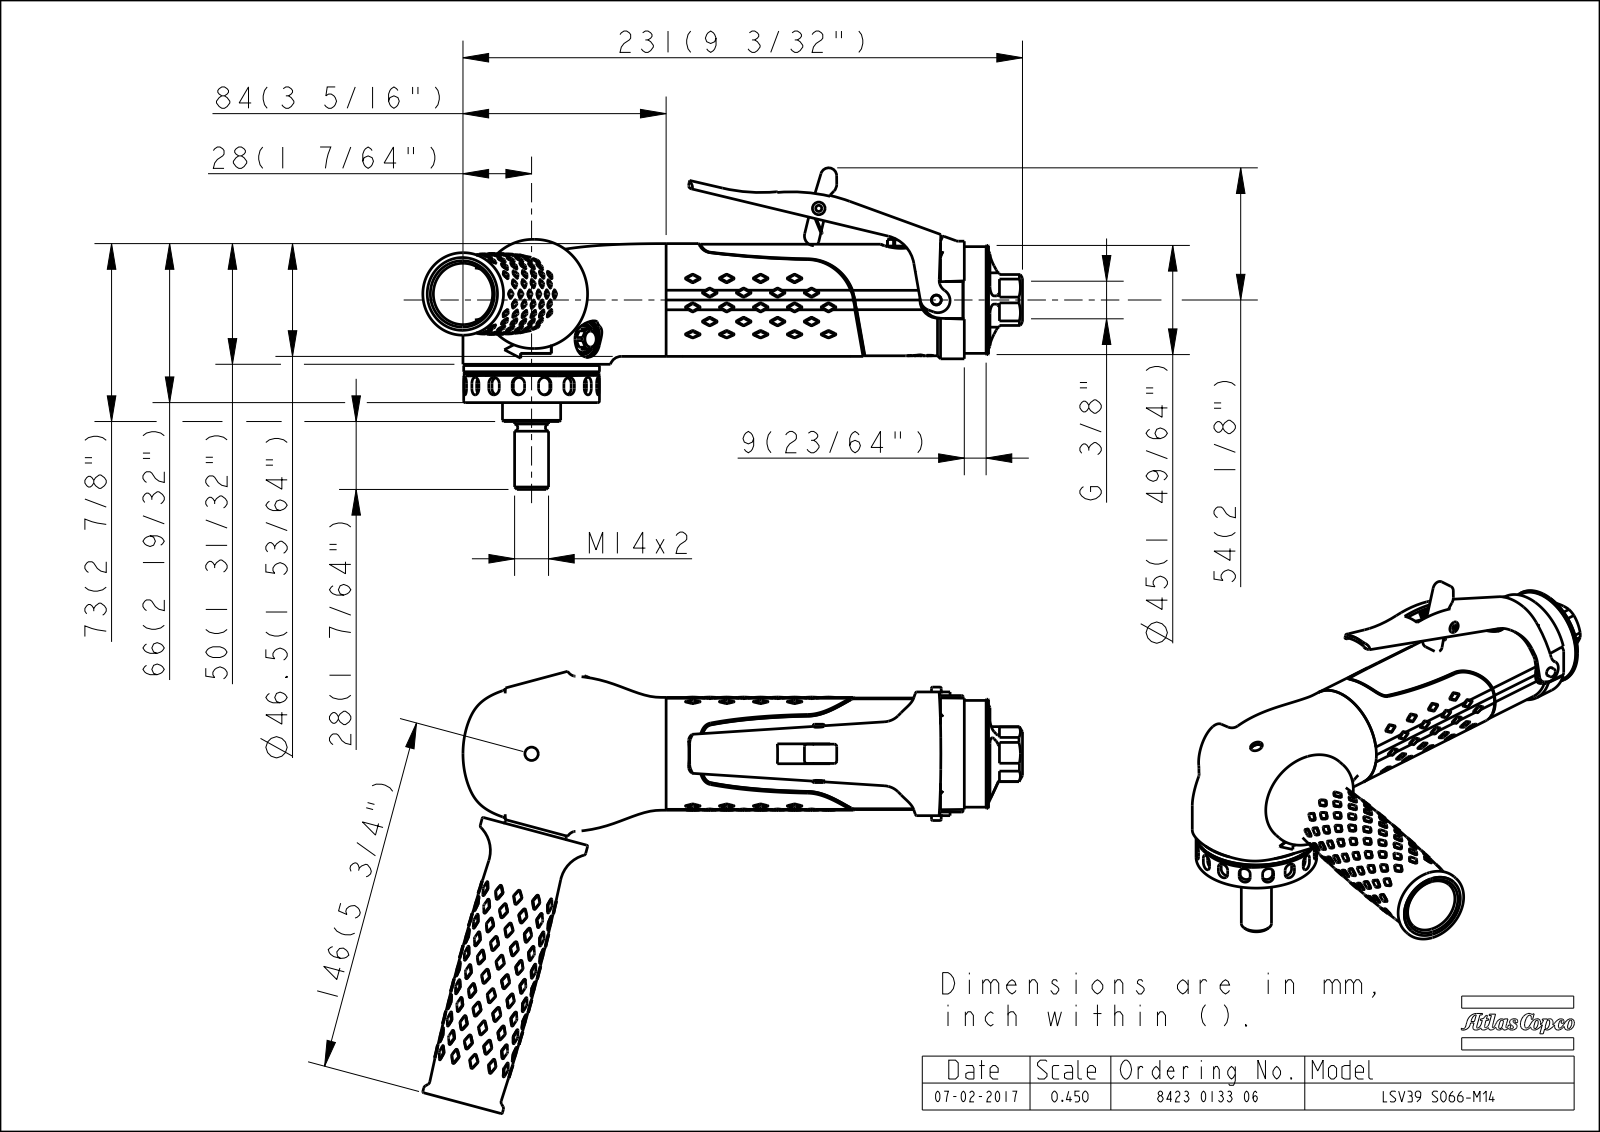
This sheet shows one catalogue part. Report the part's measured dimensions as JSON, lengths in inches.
{"part_name": "4150178903; 4150178984_ASM; 4150225400_SPEC_AF2; 4150225440_AF2 (+8 more)", "step_written_by": "CREO PARAMETRIC BY PTC INC, 2014440 (CONFIG_CONTROL_DESIGN)", "units": "inches", "bodies": {"solids": 30, "faces": 4762, "planar": 1235, "cylindrical": 1015, "other": 2512}, "overall_size": [9.739, 7.178, 5.22], "volume_in3": 16.82, "surface_area_in2": 993.2, "round_holes": [[0.118, 5], [0.197, 5], [0.165, 4], [0.492, 3], [0.106, 2], [0.217, 2], [0.331, 2], [0.335, 2], [0.591, 2], [0.047, 1], [0.094, 1], [0.098, 1]], "round_bosses_or_shafts": [[0.157, 6], [0.394, 5], [0.169, 4], [0.339, 3], [0.315, 3], [0.02, 3], [1.772, 2], [0.551, 2]], "partial_cylinders_radius": [[0.039, 255], [0.102, 32], [0.079, 25], [0.02, 24], [0.118, 14], [0.028, 12], [0.098, 7], [0.197, 7]], "face_to_face_distances": [0.059, 0.622, 0.024, 1.8, 0.039, 0.335, 0.098, 0.433, 0.13, 0.61], "hole_center_spacings": [0.157, 0.964, 1.364, 0.642, 1.929, 5.361, 5.362, 6.715]}
